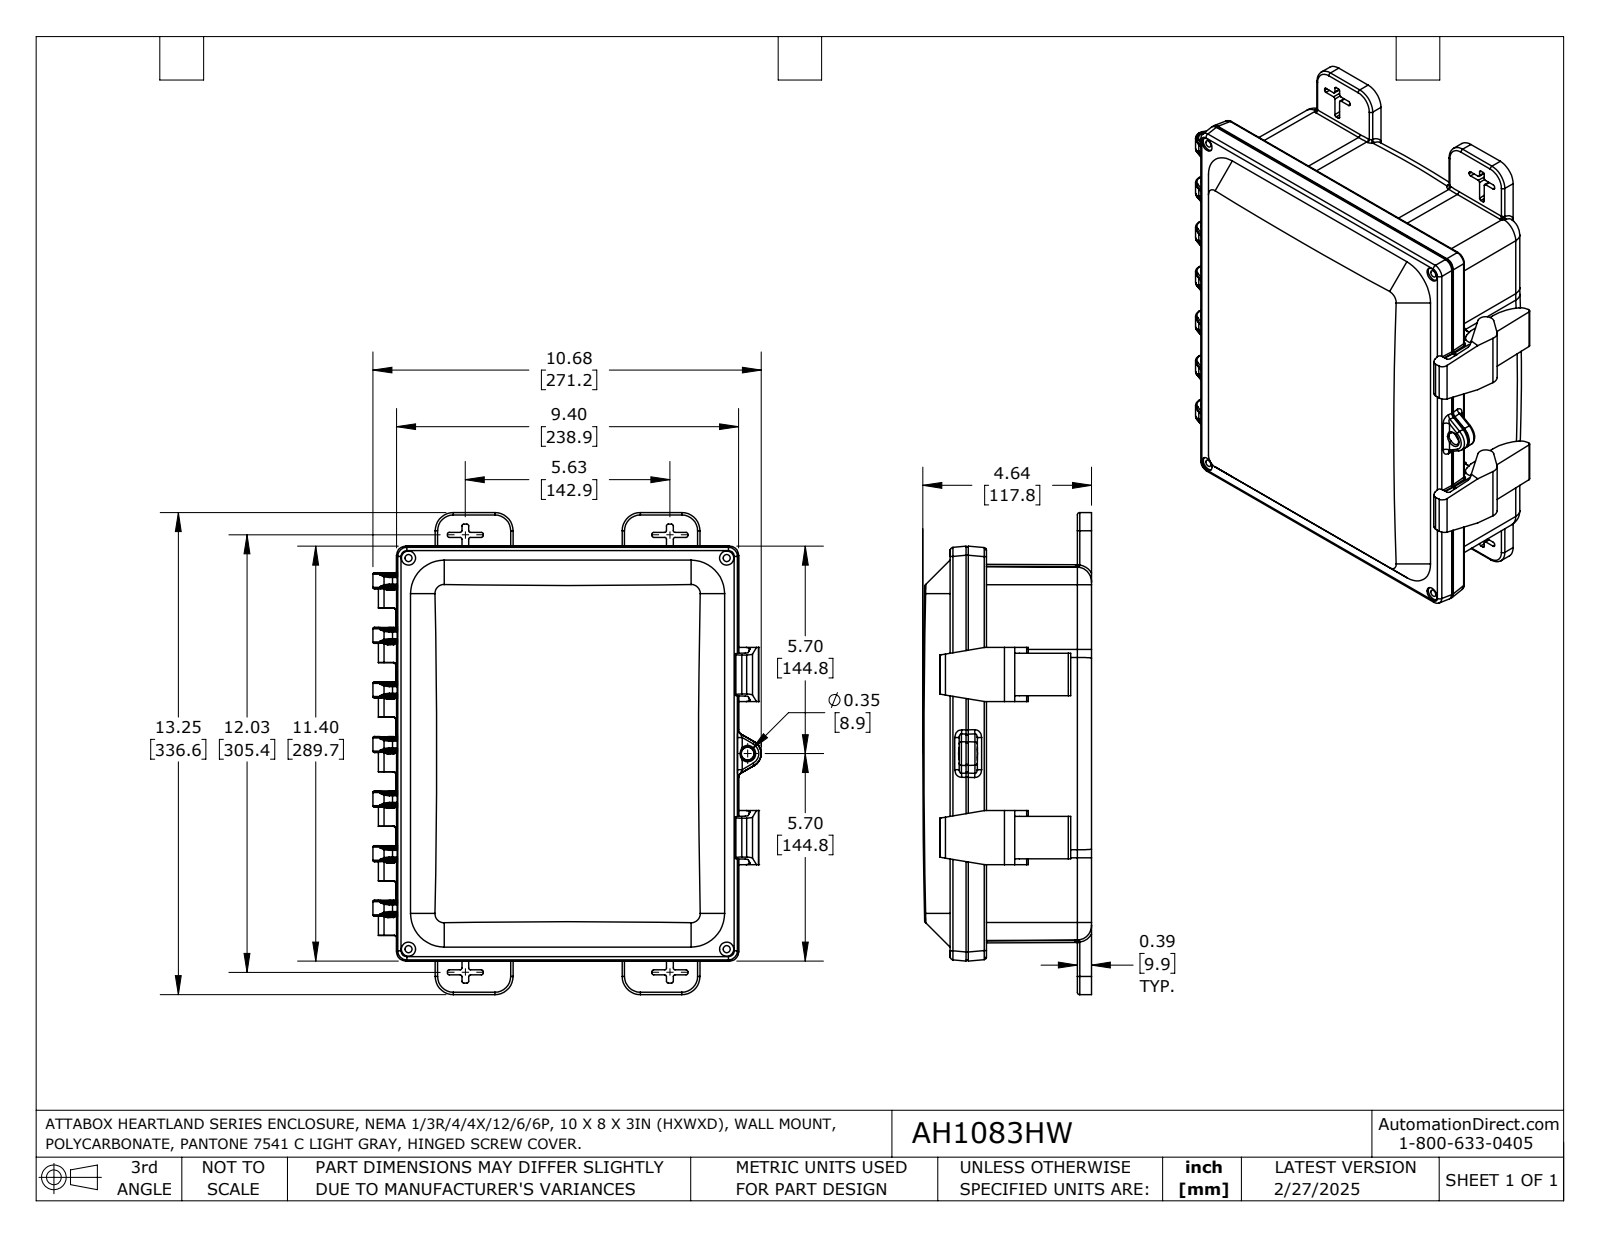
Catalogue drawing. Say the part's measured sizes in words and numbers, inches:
The part is named "AH1083HW". Its 3-D file was written by "SolidWorks 2024 (AUTOMOTIVE_DESIGN)". It is 6 solids with 1802 faces: 487 planar, 570 cylindrical and 745 other. Overall it measures 13.25 by 10.676 by 4.676 inches. Its volume is 76.36 cubic inches and its surface area 868.2 square inches. Round holes: 11 of diameter 0.179, 4 of diameter 0.195, 4 of diameter 0.286, 4 of diameter 0.296, 4 of diameter 0.39, 1 of diameter 0.327, 1 of diameter 0.375, 1 of diameter 0.45. Round bosses or shafts: 11 of diameter 0.496, 4 of diameter 0.638, 1 of diameter 0.313. Partial cylindrical surfaces (rounded edges, fillets, slot ends): 128 of radius 0.035, 85 of radius 0.065, 26 of radius 0.025, 25 of radius 0.01, 16 of radius 0.02, 12 of radius 0.5, 9 of radius 0.13, 8 of radius 0.125. The main face-to-face distances are 0.11, 3.39, 3.28, 0.5, 0.133, 2.89, 2.78, 0.15, 7.998, 0.35. The hole center spacings are 3.125, 3.743, 5.171, 1.767, 2.06, 3.743, 4.12, 6.25.
